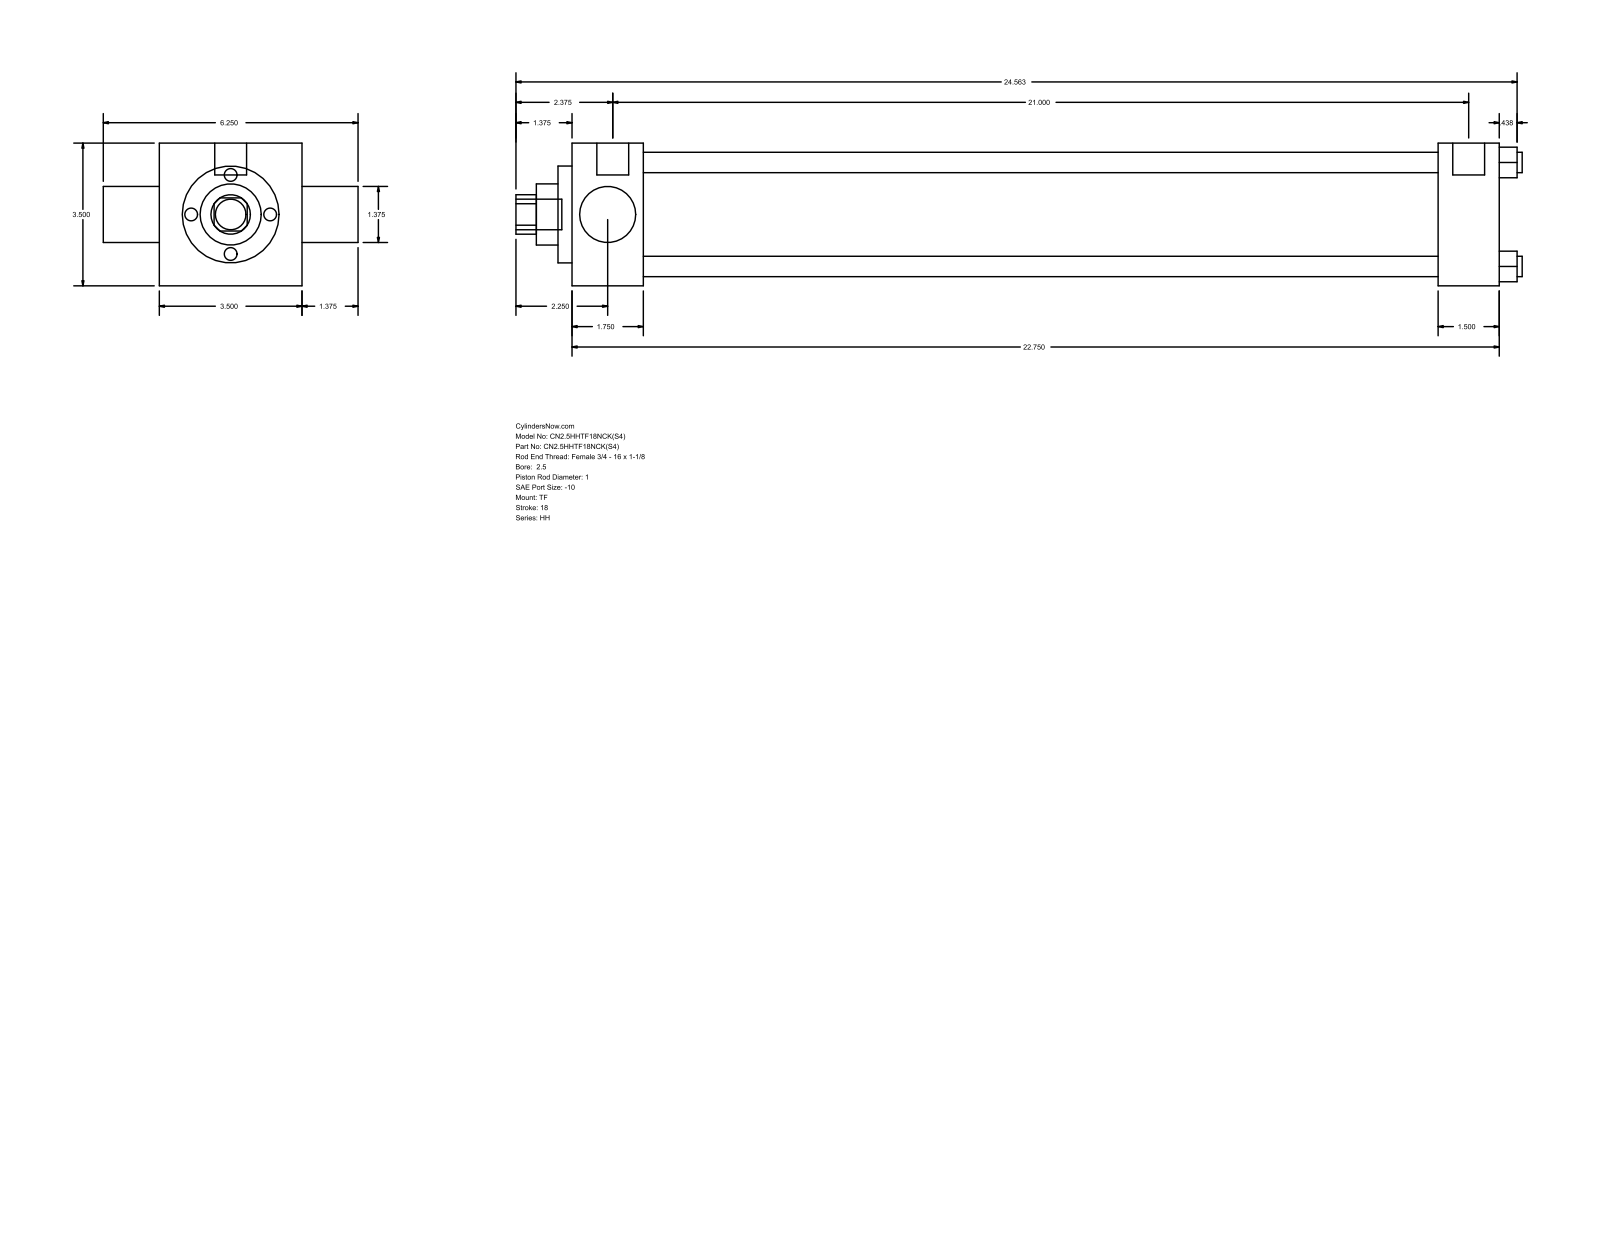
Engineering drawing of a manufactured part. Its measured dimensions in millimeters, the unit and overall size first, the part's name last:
Units: millimetres
Overall size (bounding box): 627.06 × 158.75 × 88.9
Round holes (diameter × count): ⌀12.7 ×4, ⌀25.4 ×1, ⌀34.92 ×1, ⌀38.1 ×1, ⌀60.33 ×1, ⌀73.03 ×1
Round bosses / shafts (diameter × count): ⌀5.56 ×3, ⌀19.84 ×2, ⌀19.05 ×1
Partial cylindrical surfaces — rounded edges, fillets, slot ends (radius × count): R12.29 ×1
Main face-to-face distances: 88.9, 577.85, 44.46, 533.39, 539.75, 495.29, 38.1, 34.93, 123.83, 8.73
Hole centre spacings: 45.79, 64.76, 91.58
Bodies: 0 solids, 86 faces (61 planar, 25 cylindrical, 0 other)
Part name (STEP PRODUCT): HH_TF__0250_1
STEP written by: GSSL Pune (CONFIG_CONTROL_DESIGN)
